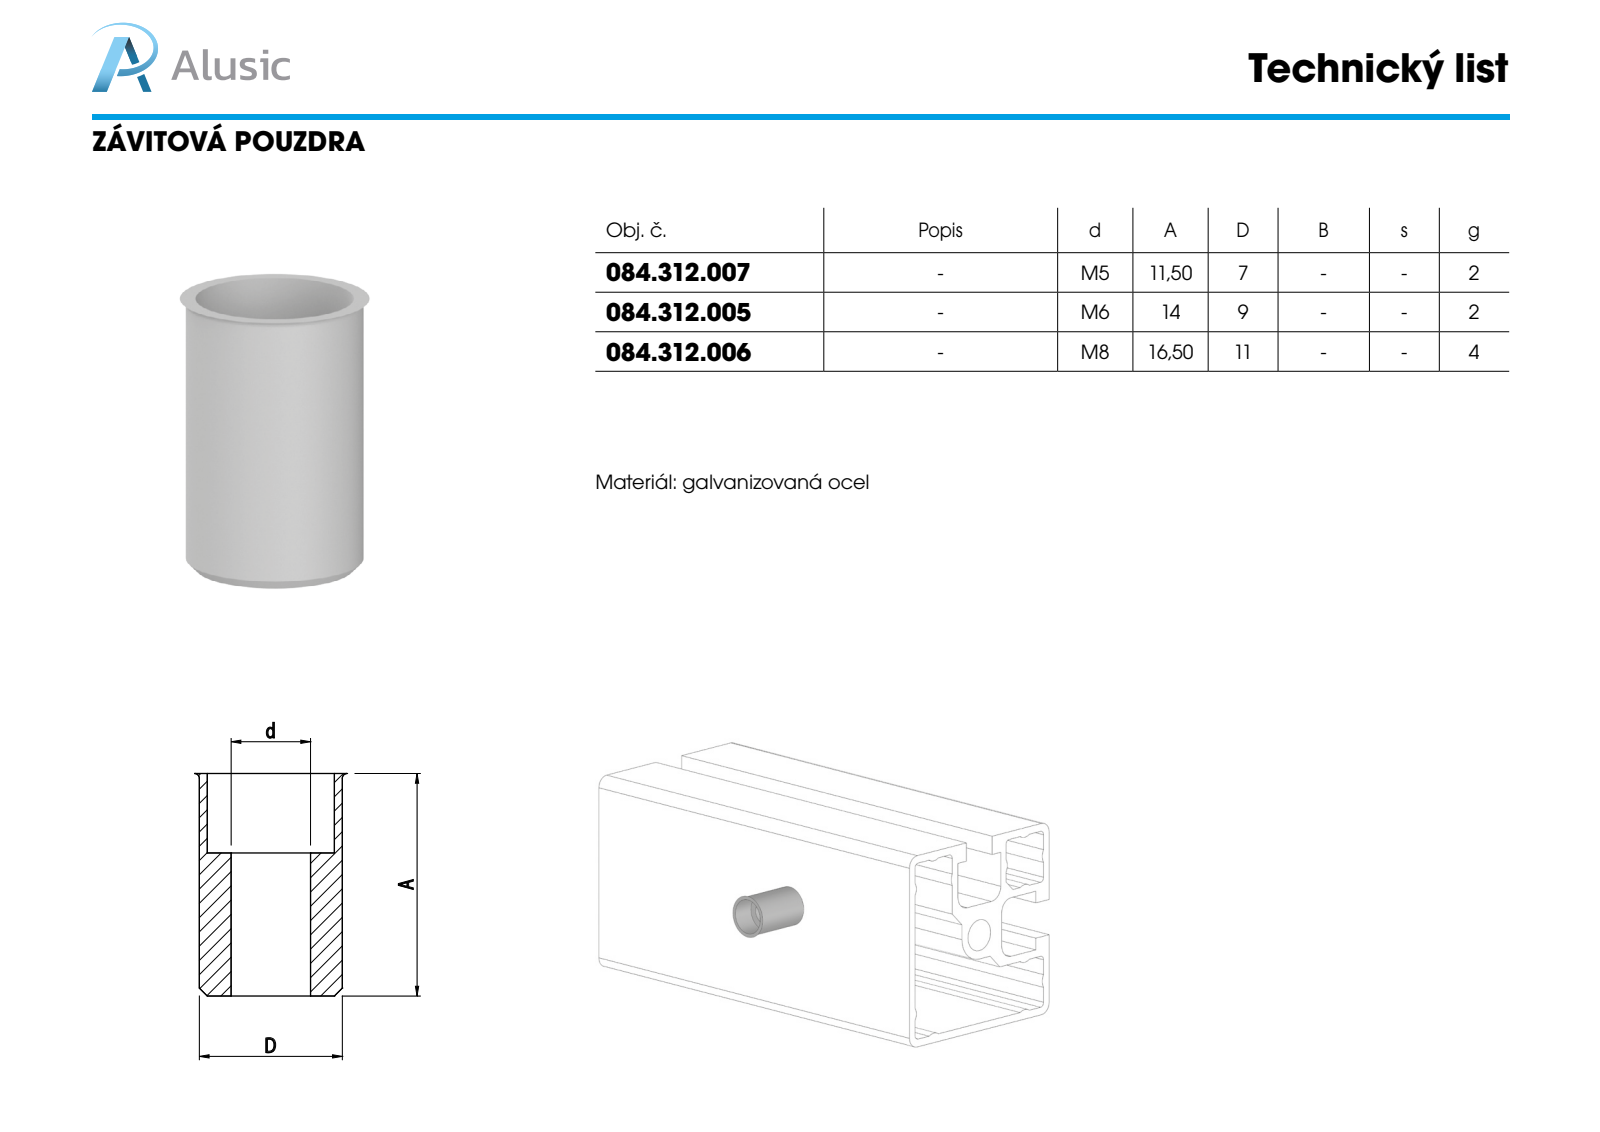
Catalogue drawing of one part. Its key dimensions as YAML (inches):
part_name: "084.312.007"
step_written_by: "SolidWorks 2016 (CONFIG_CONTROL_DESIGN)"
units: inches
bodies: {solids: 1, faces: 13, planar: 3, cylindrical: 6, other: 4}
overall_size: [0.453, 0.299, 0.299]
volume: 0.01
surface_area: 0.761
round_holes:
  - {diameter: 0.197, count: 1}
  - {diameter: 0.236, count: 1}
round_bosses_or_shafts:
  - {diameter: 0.276, count: 1}
face_to_face_distances: [0.197, 0.256, 0.453]
